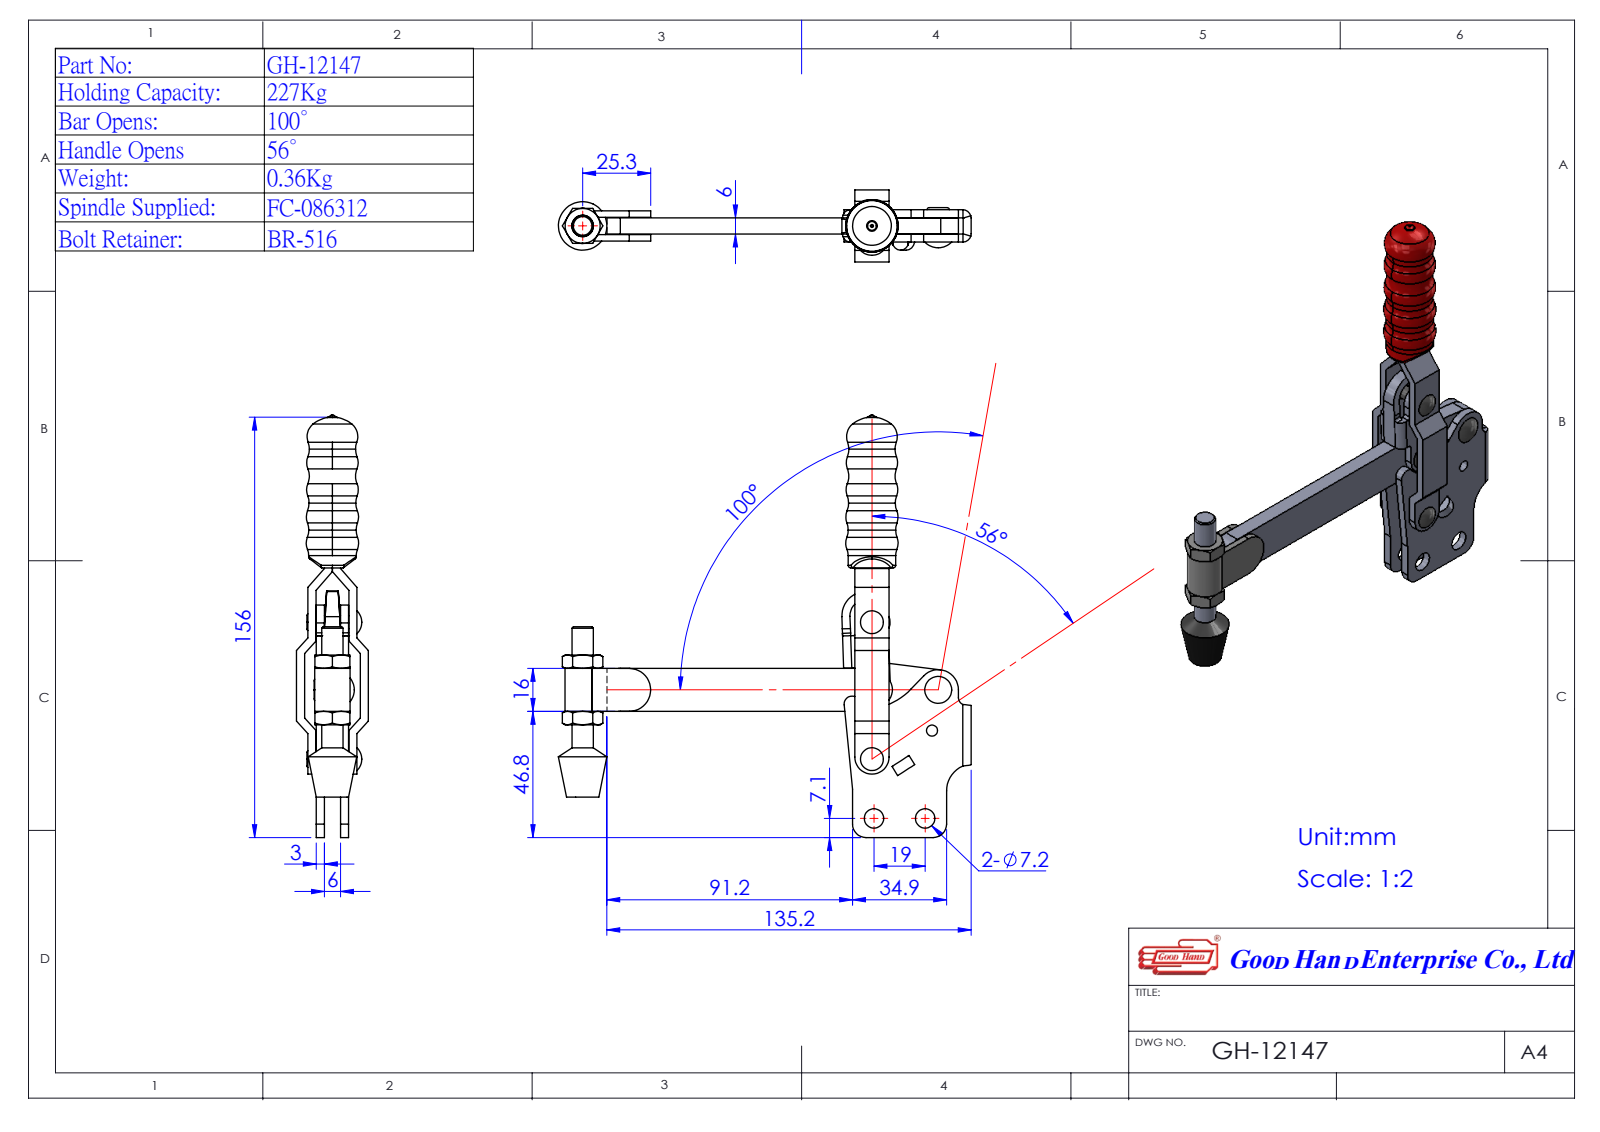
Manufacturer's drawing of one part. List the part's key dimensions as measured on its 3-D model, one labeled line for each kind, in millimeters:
Part name (STEP PRODUCT): 11214208-1^EMC12147; Group5^EMC12147; EMC12147; Group1^EMC12147 (+2 more)
STEP written by: SolidWorks 2016 (AUTOMOTIVE_DESIGN)
Units: millimetres
Bodies: 5 solids, 307 faces (130 planar, 92 cylindrical, 85 other)
Overall size (bounding box): 156.16 × 153.29 × 26.7
Volume: 58 718 mm³ · Surface area: 33 282 mm²
Round holes (diameter × count): ⌀4.5 ×4, ⌀7.2 ×2
Round bosses / shafts (diameter × count): ⌀17.61 ×1, ⌀7.93 ×1
Partial cylindrical surfaces — rounded edges, fillets, slot ends (radius × count): R5 ×4, R7.5 ×4, R0.1 ×2, R1 ×2, R2.42 ×2, R3 ×2, R3.1 ×2, R6.4 ×2
Main face-to-face distances: 3, 9, 6, 12, 12.1, 3.1, 7.35, 16.35, 19.45, 4.25
Hole centre spacings: 19, 22.01, 23.4, 25.13, 25.73, 29.56, 35.14, 35.58
